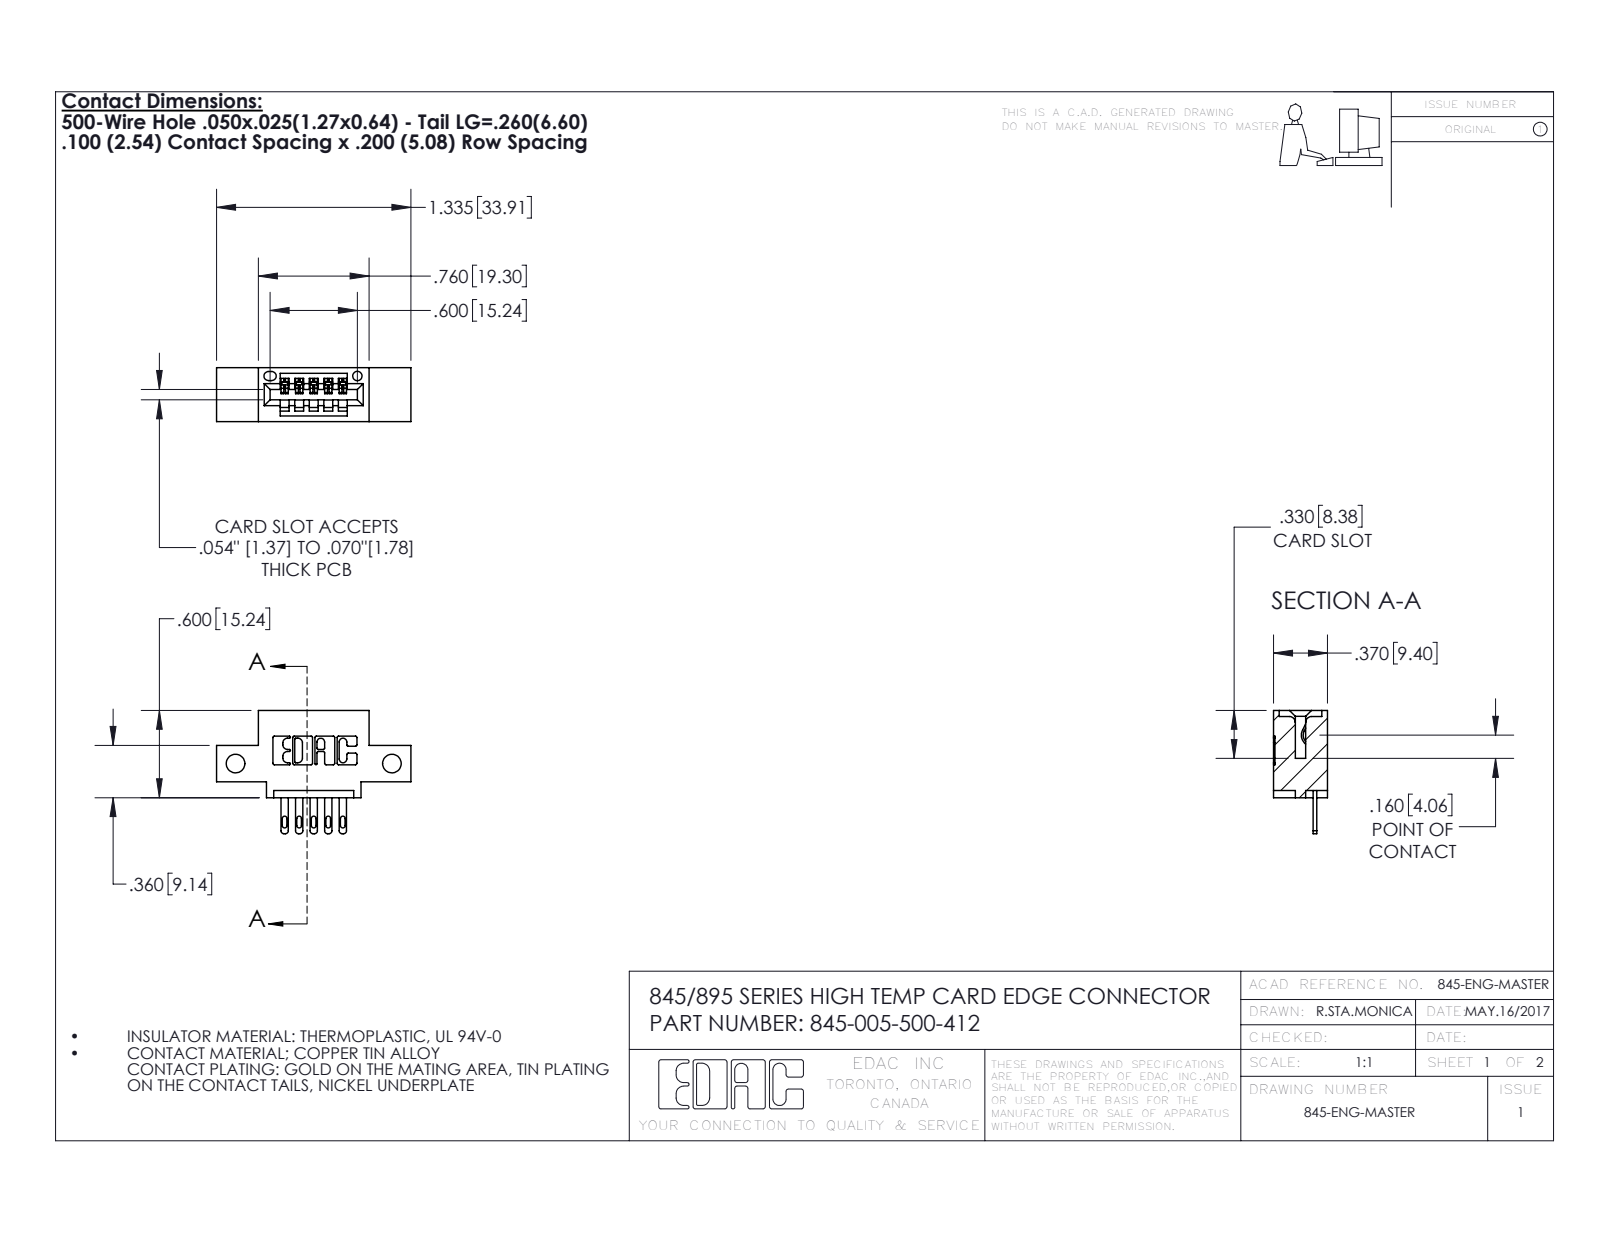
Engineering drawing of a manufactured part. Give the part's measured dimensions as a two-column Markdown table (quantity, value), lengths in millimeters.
| quantity | value |
| --- | --- |
| part name | 345-292-001_345-293-100; 345 Part_0.110 Offset - Side Mount; 345-005-500-412 |
| STEP written by | SolidWorks 2016 (CONFIG_CONTROL_DESIGN) |
| units | millimeters |
| bodies | 6 solids, 400 faces (254 planar, 146 cylindrical, 0 other) |
| overall size | 33.9 × 21.5 × 9.4 |
| volume | 2 750 mm³ |
| surface area | 3 116 mm² |
| round holes (diameter × count) | 3.3 × 2, 1.6 × 1 |
| partial cylindrical surfaces (radius × count) | 0.3 × 22, 0.2 × 10, 0.4 × 10, 0.5 × 10, 0.2 × 6, 0.8 × 6, 0.7 × 3, 0.8 × 2 |
| main face-to-face distances | 5.1, 9.4, 1.8, 7.6, 2.5, 6.4, 0.6, 2.5, 6.9, 1.5 |
| hole center spacings | 27.3 |
